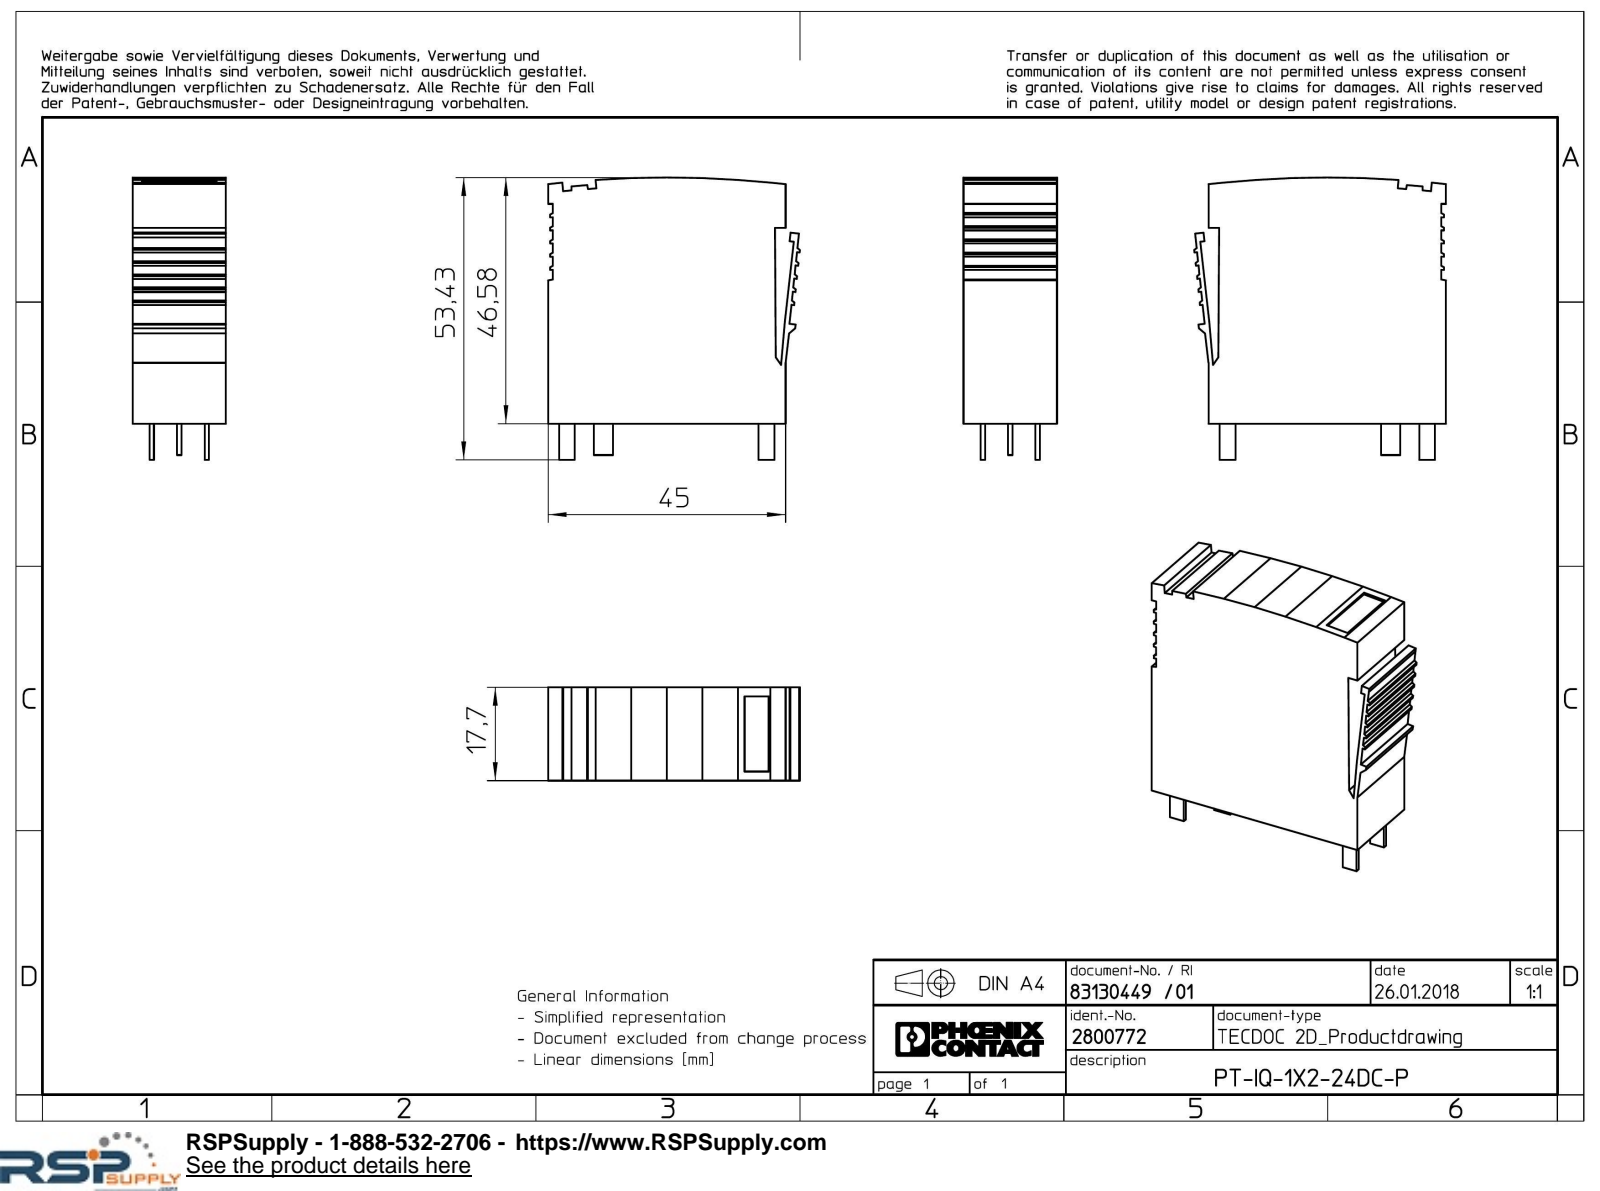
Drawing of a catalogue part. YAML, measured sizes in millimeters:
part_name: "PT_IQ_1X2_24DC_P-select"
step_written_by: "Creo Elements/Direct Modeling 18.1I 14-Aug-2016 (C) Parametric Technology GmbH (AUTOMOTIVE_DESIGN)"
units: millimeters
bodies: {solids: 1, faces: 154, planar: 148, cylindrical: 6, other: 0}
overall_size: [53.42, 47.71, 17.7]
volume: 35037
surface_area: 9408
partial_cylinders:
  - {radius: 0.3, count: 4}
  - {radius: 1.48, count: 2}
face_to_face_distances: [17.7, 45, 0.9, 44.1, 1.1, 16.6, 0.8, 5.05, 12.65, 6.34]
